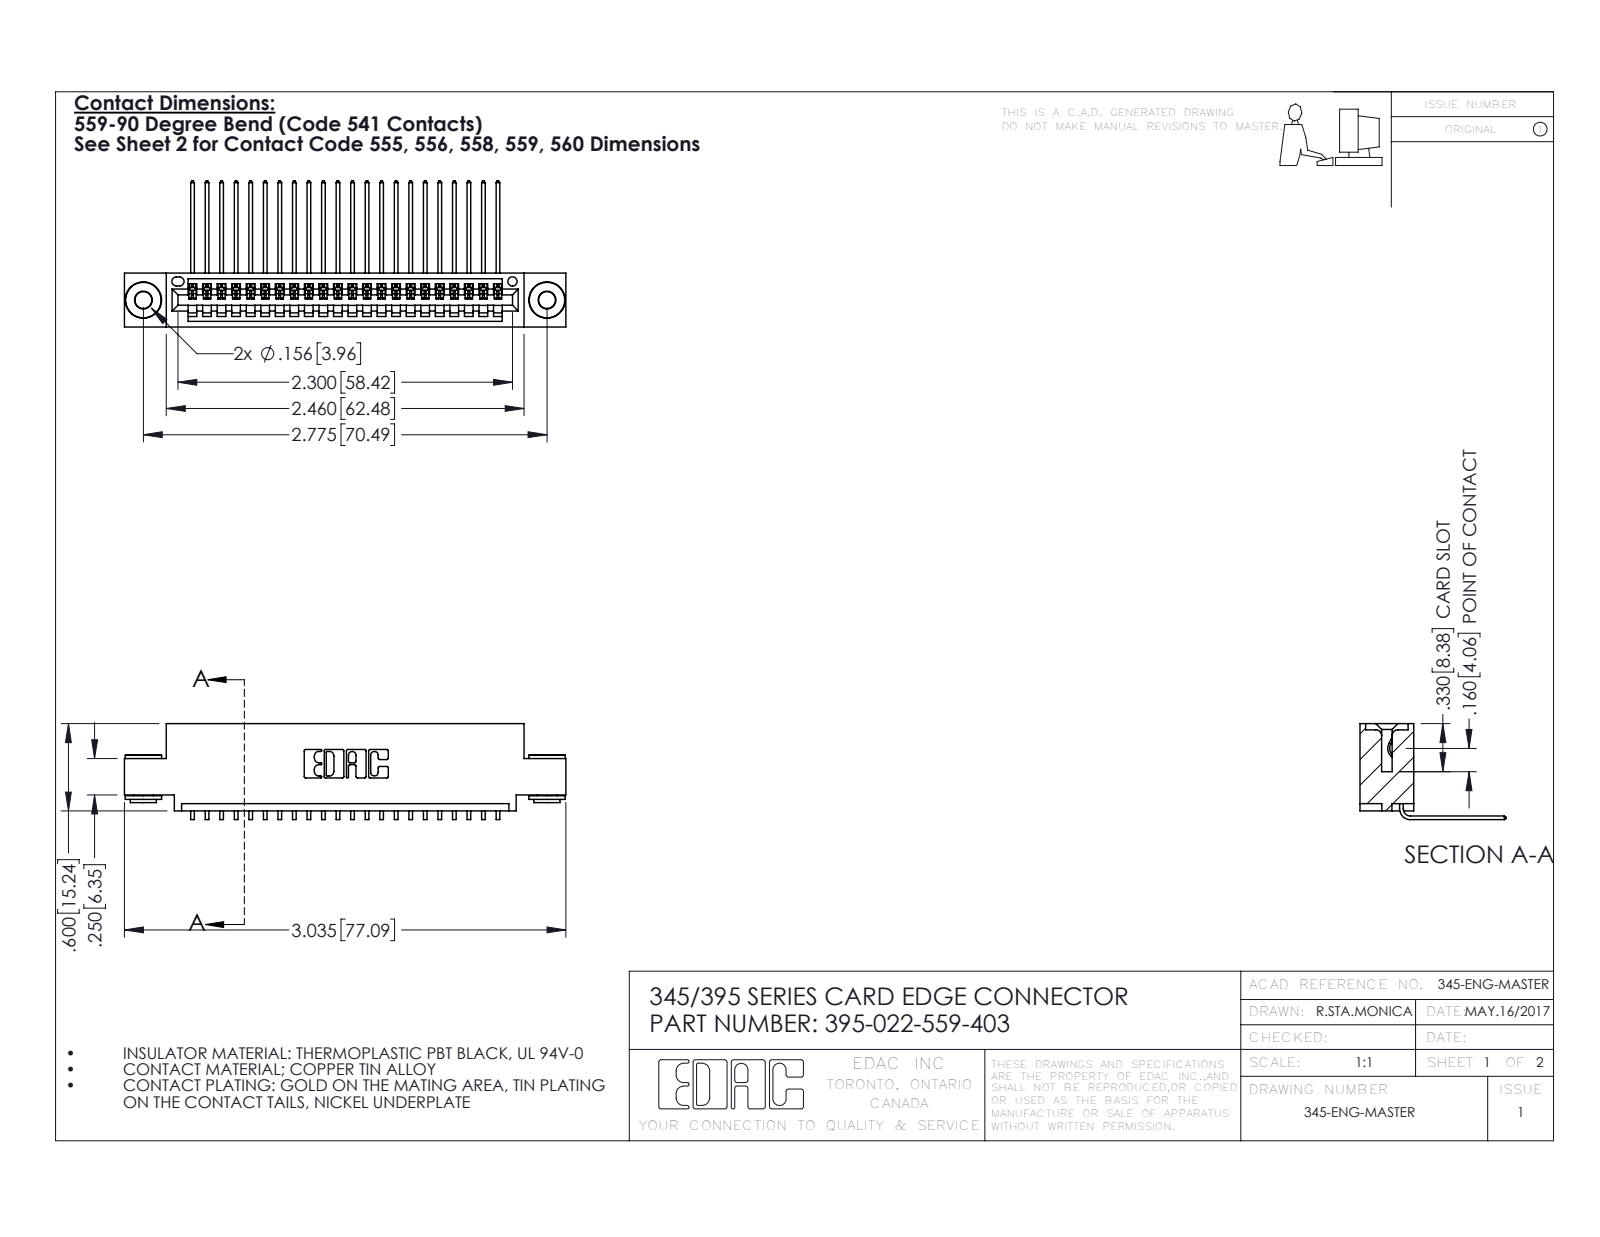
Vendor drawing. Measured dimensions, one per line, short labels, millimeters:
name: 345-292-001_558 559 Tail - 1; 345 Part_0.110 Offset - 0.156 Dia-TH; 395-022-559-403; 345-250-002_345-250-002-102
written by: SolidWorks 2016 (CONFIG_CONTROL_DESIGN)
unit: mm
bodies: 25 solids, 1488 faces (1018 planar, 462 cylindrical, 8 other)
size: 77.1 × 25.5 × 16.7
volume: 7 180 mm³; area: 9 994 mm²
holes: 2× ⌀2.9, 2× ⌀4, 1× ⌀1.6
bosses: 2× ⌀6.4, 2× ⌀4.6, 2× ⌀3.5
rounds: 44× R0.2, 22× R0.3, 6× R0.2, 6× R0.8, 3× R0.7, 2× R0.8, 2× R1, 1× R0.4
face distances: 1.8, 7.6, 9.4, 5.1, 0.6, 2.5, 6.9, 5.7, 3.8, 1.8
hole spacings: 6.9, 64.5, 70.5
